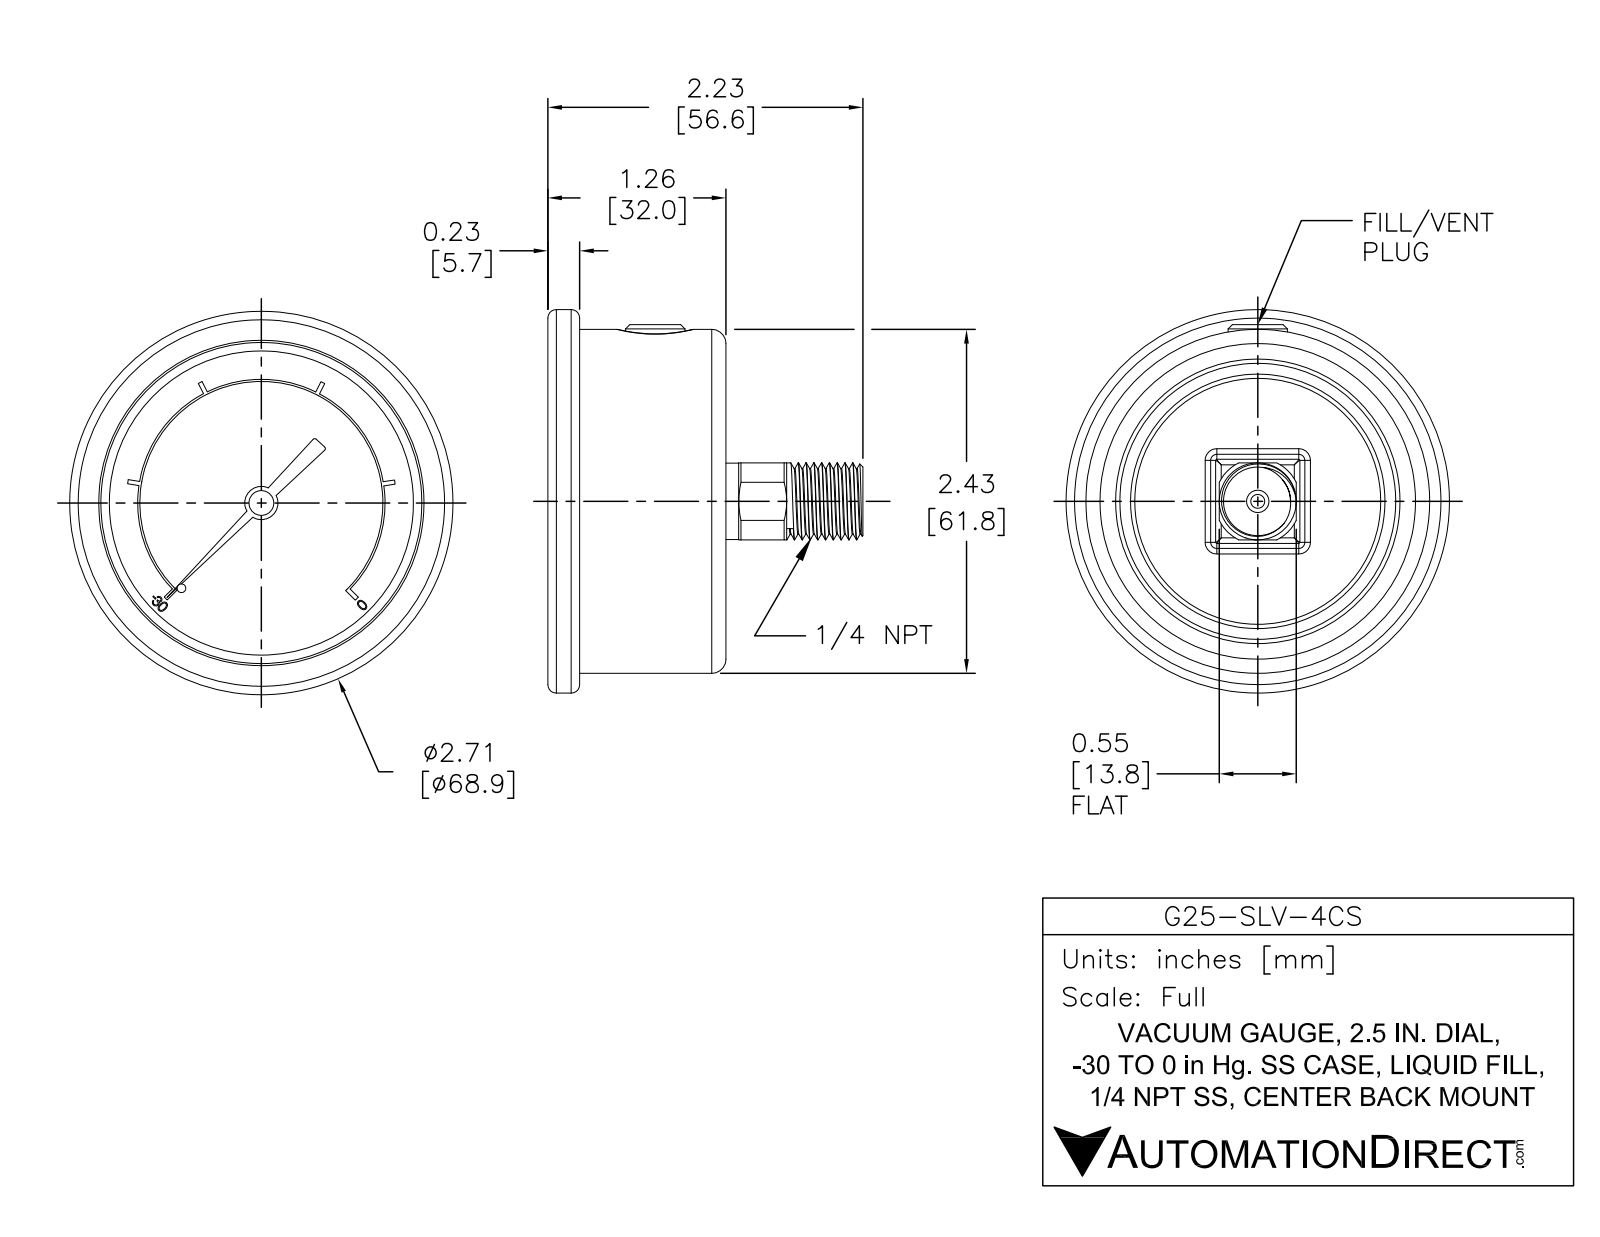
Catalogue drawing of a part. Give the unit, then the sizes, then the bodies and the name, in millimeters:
Units: millimetres
Overall size (bounding box): 68.9 × 68.9 × 56.6
Round holes (diameter × count): ⌀1.8 ×1, ⌀2.5 ×1, ⌀57.7 ×1
Round bosses / shafts (diameter × count): ⌀68.9 ×1, ⌀61.8 ×1, ⌀13.8 ×1, ⌀13.7 ×1, ⌀10.7 ×1, ⌀6 ×1, ⌀4.5 ×1, ⌀3.6 ×1
Partial cylindrical surfaces — rounded edges, fillets, slot ends (radius × count): R1.5 ×8, R0.4 ×2, R7.7 ×1, R21.8 ×1, R22.2 ×1
Main face-to-face distances: 24.1, 30.5, 6.4, 1.5, 25.7, 32, 26.3, 24.8, 0.6, 5.7
Volume: 84 690 mm³ · Surface area: 16 010 mm²
Bodies: 1 solid, 353 faces (208 planar, 83 cylindrical, 62 other)
Part name (STEP PRODUCT): G25-SLV-4CS
STEP written by: SolidWorks 2021 (AUTOMOTIVE_DESIGN)
